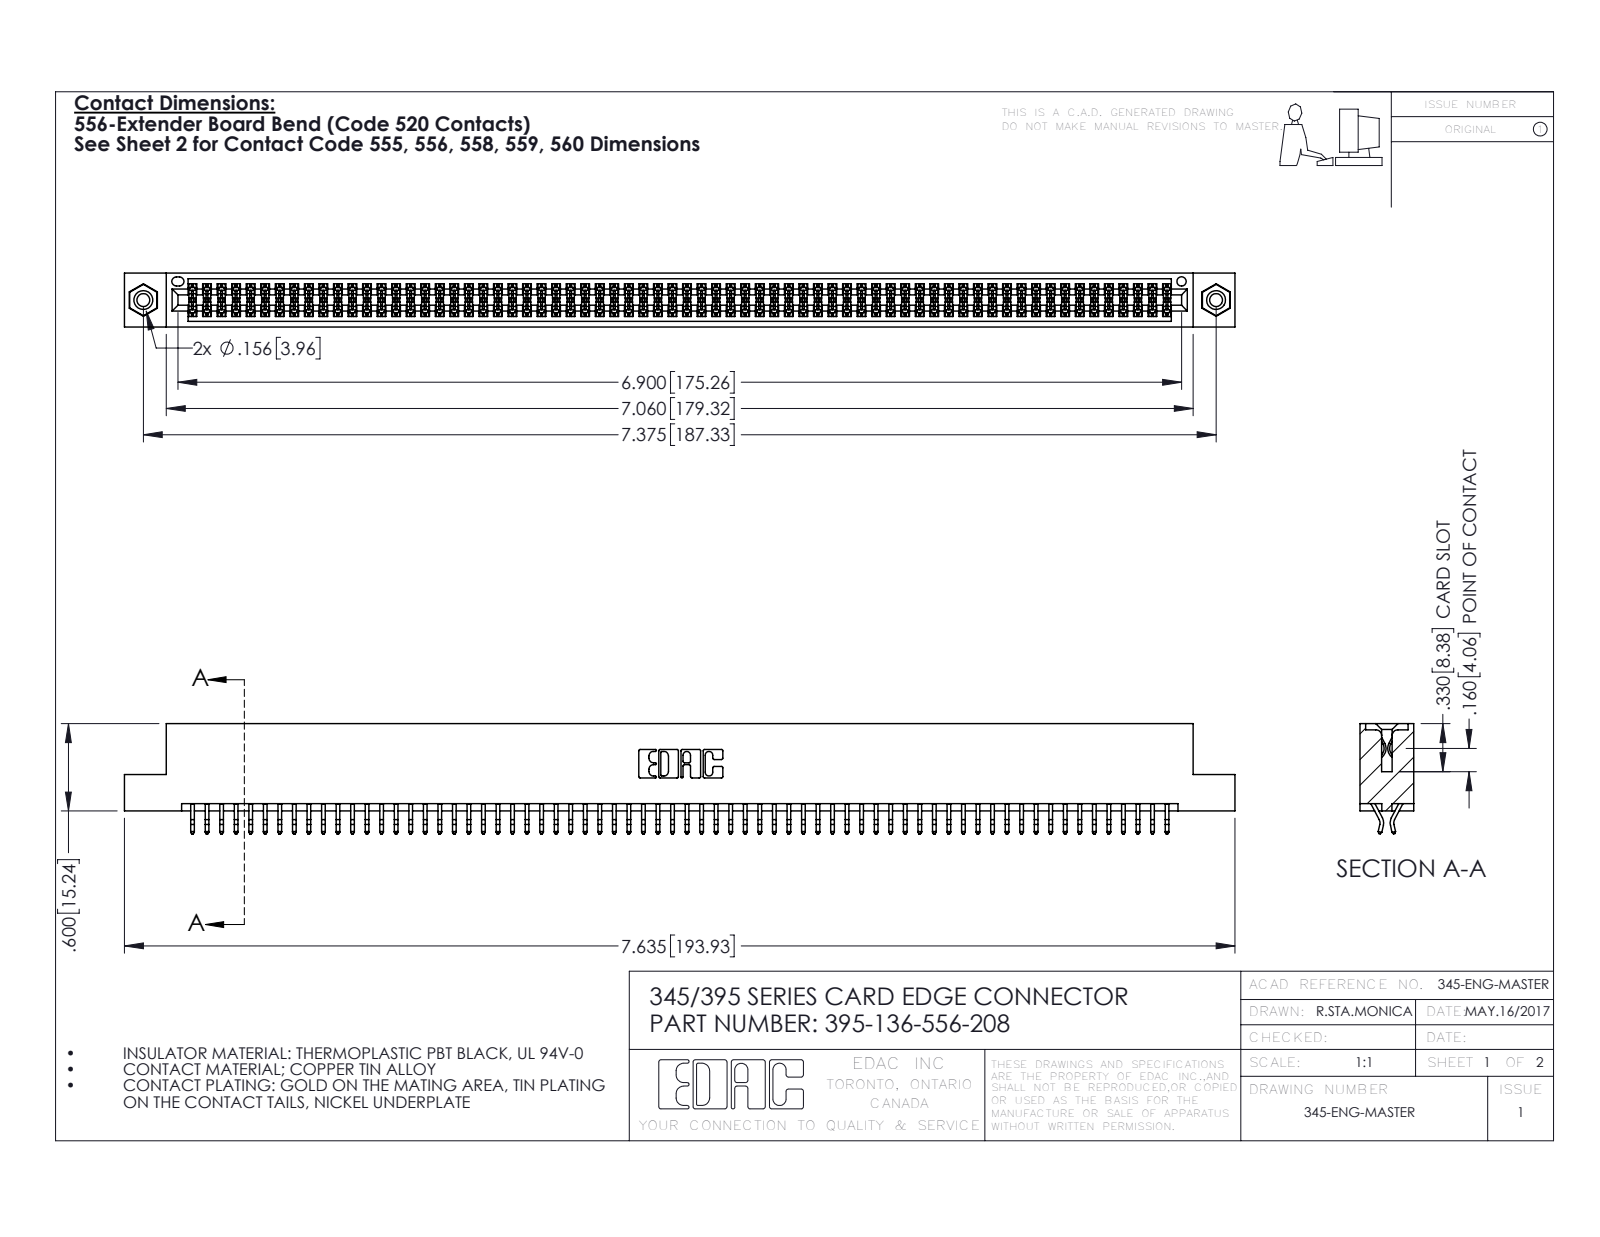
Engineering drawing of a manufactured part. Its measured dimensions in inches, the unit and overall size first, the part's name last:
Units: inches
Overall size (bounding box): 7.635 × 0.757 × 0.37
Round holes (diameter × count): ⌀0.089 ×2, ⌀0.125 ×2, ⌀0.156 ×2, ⌀0.064 ×1
Round bosses / shafts (diameter × count): ⌀0.155 ×2
Partial cylindrical surfaces — rounded edges, fillets, slot ends (radius × count): R0.006 ×204, R0.01 ×22, R0.007 ×6, R0.031 ×6, R0.026 ×3, R0.01 ×2, R0.014 ×2, R0.019 ×2
Main face-to-face distances: 0.072, 0.298, 0.37, 0.2, 0.025, 0.098, 0.272, 0.225, 0.175, 0.149
Hole centre spacings: 0.27, 7.139, 7.375
Volume: 1.164 in³ · Surface area: 44.3 in²
Bodies: 139 solids, 7802 faces (5144 planar, 2642 cylindrical, 16 other)
Part name (STEP PRODUCT): 395-136-556-208; 345-292-001_556 Tail; 345 Part_Flush Mounting Lugs - 0.156 Dia-TI; 345-250-001_345-250-003-102
STEP written by: SolidWorks 2016 (CONFIG_CONTROL_DESIGN)
